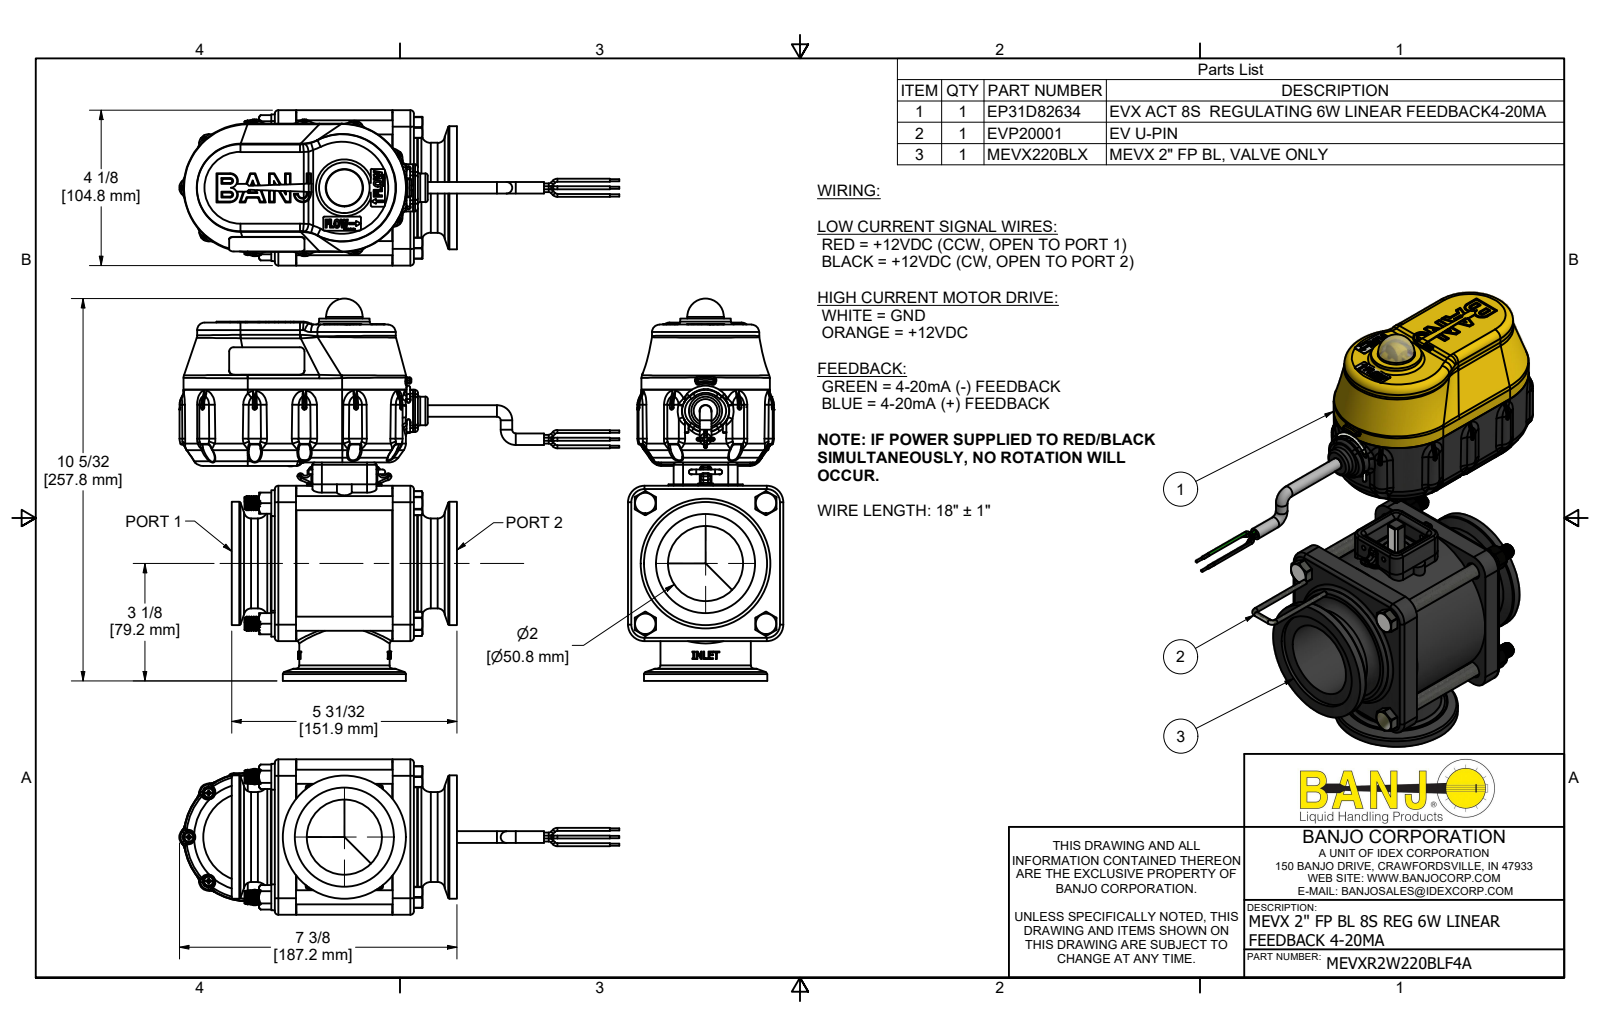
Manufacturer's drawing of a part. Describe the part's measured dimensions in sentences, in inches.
The part is named "MEVXR2W220BLF4A; EP31D82634; B61905PPHS; EP20KIT (+8 more)". Its 3-D file was written by "Autodesk Inventor 2022 (AUTOMOTIVE_DESIGN)". It is 626 solids with 18691 faces: 7226 planar, 6230 cylindrical and 5235 other. Overall it measures 11.685 by 10.15 by 4.125 inches. Its volume is 76.35 cubic inches and its surface area 797.1 square inches. Round holes: 184 of diameter 0.01, 27 of diameter 0.009, 27 of diameter 0.012, 12 of diameter 0.029, 11 of diameter 0.019, 11 of diameter 0.095, 11 of diameter 0.15, 10 of diameter 0.076, 7 of diameter 0.033, 6 of diameter 0.017, 6 of diameter 0.067, 4 of diameter 0.097. Round bosses or shafts: 167 of diameter 0.026, 60 of diameter 0.324, 27 of diameter 0.028, 20 of diameter 0.08, 17 of diameter 0.25, 11 of diameter 0.14, 11 of diameter 0.108, 11 of diameter 0.085. Partial cylindrical surfaces (rounded edges, fillets, slot ends): 152 of radius 0.04, 89 of radius 0.02, 76 of radius 0.01, 74 of radius 0.005, 52 of radius 0.004, 39 of radius 0.03, 32 of radius 0.015, 28 of radius 0.008. The main face-to-face distances are 0.1, 0.078, 0.076, 2.565, 2.4, 1.417, 0.08, 0.56, 3.13, 0.537. The hole center spacings are 1.283, 2.265, 3.204, 2.73, 2.967, 3.45, 4.214, 0.487.
